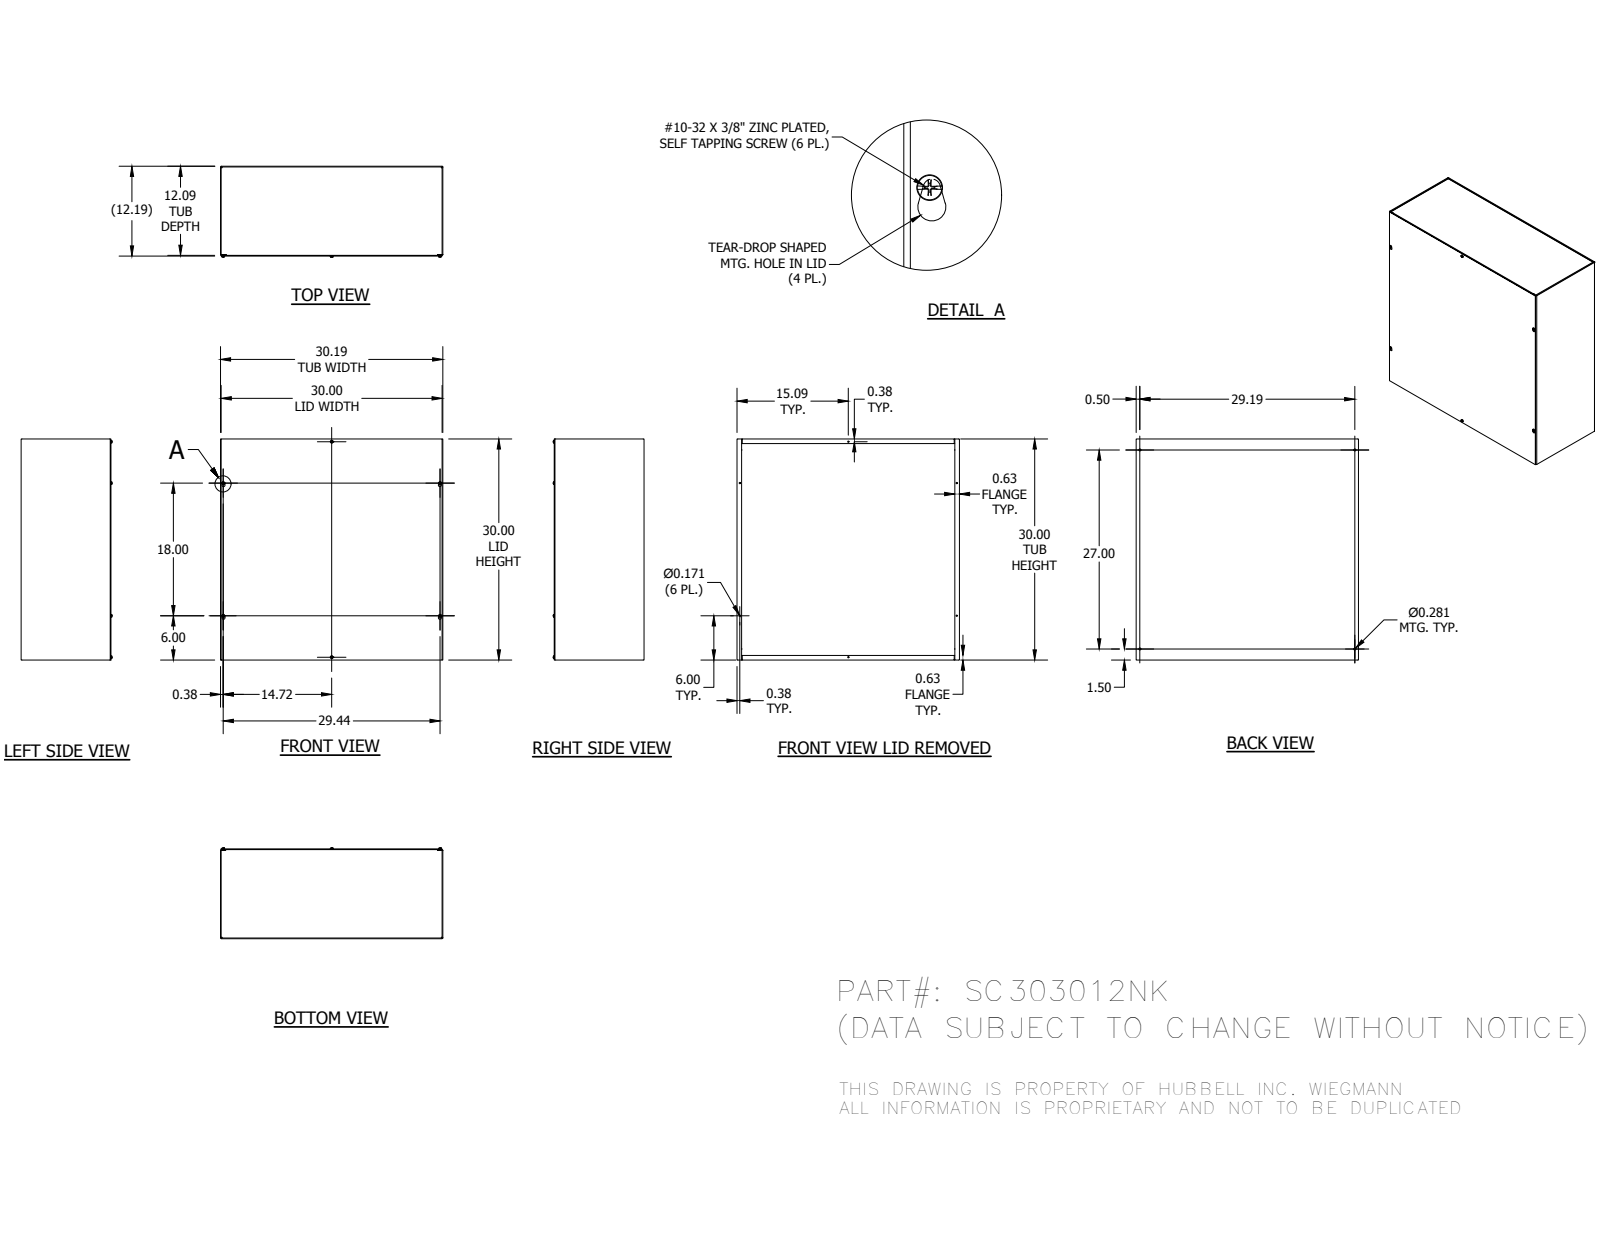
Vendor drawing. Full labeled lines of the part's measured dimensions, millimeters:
Part name (STEP PRODUCT): SC303012NKBLR; SC3012NKTB; SC3030LPA; 37214 (+1 more)
STEP written by: Autodesk Inventor 2014 (AUTOMOTIVE_DESIGN)
Units: millimetres
Bodies: 10 solids, 404 faces (232 planar, 50 cylindrical, 122 other)
Overall size (bounding box): 766.76 × 762 × 312.91
Volume: 5 157 000 mm³ · Surface area: 4 361 000 mm²
Round holes (diameter × count): ⌀4.34 ×6, ⌀7.14 ×4, ⌀7.92 ×2
Round bosses / shafts (diameter × count): ⌀4.83 ×6
Partial cylindrical surfaces — rounded edges, fillets, slot ends (radius × count): R0.4 ×12, R2.78 ×12, R3.17 ×4, R5.16 ×4
Main face-to-face distances: 2.38, 307.18, 304.8, 309.56, 762, 759.62, 764.38, 757.24, 766.76, 4.76
Hole centre spacings: 114.34, 371.78, 400.23, 571.51, 707.01, 753.26, 804.82, 938.59
